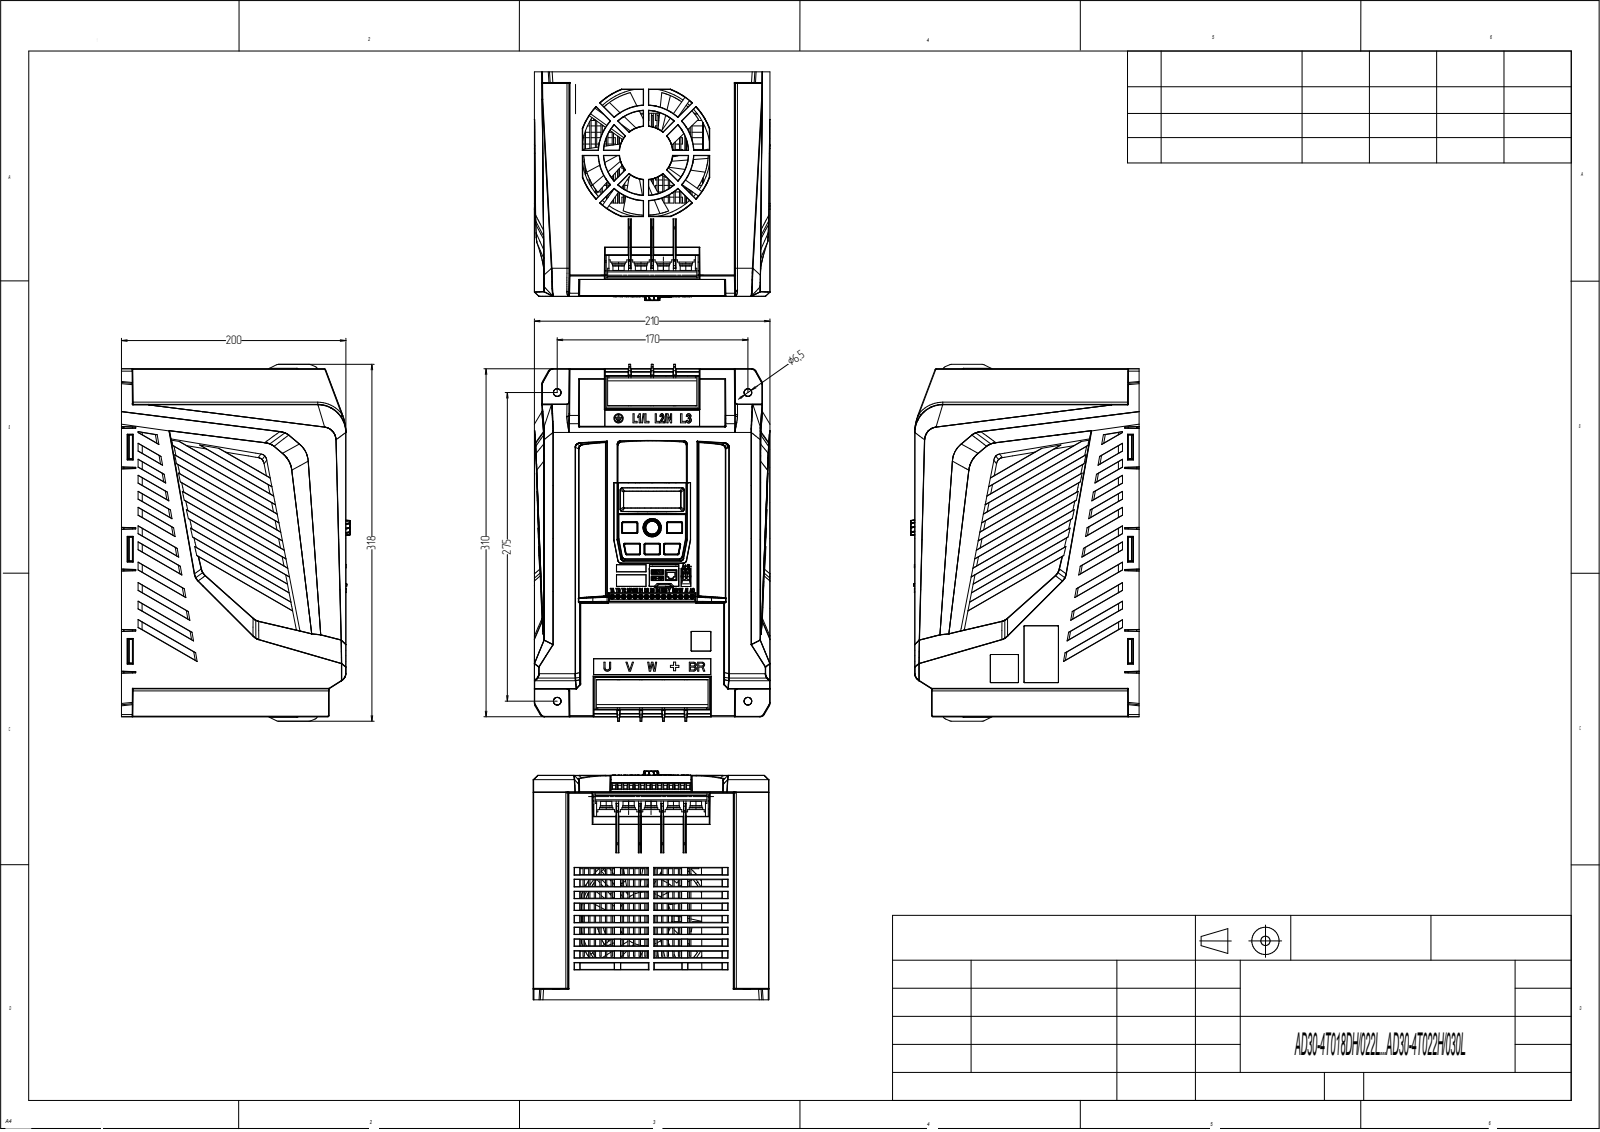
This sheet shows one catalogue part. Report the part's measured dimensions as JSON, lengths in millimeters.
{"part_name": "it3F445D75qg3i", "step_written_by": "SIEMENS PLM Software NX 10.0 (AP203_CONFIGURATION_CONTROLLED_3D_DESIGN_OF_MECHANICAL_PARTS_AND_ASSEMBLIES_MIM_LF)", "units": "millimeters", "bodies": {"solids": 137, "faces": 14429, "planar": 9729, "cylindrical": 2018, "other": 2682}, "overall_size": [318, 210, 203.79], "volume_mm3": 3156000, "surface_area_mm2": 2460000, "round_holes": [[4.1, 19], [1.4, 16], [3.1, 15], [5, 9], [6.1, 9], [6.4, 9], [4.5, 8], [3.7, 5], [2, 4], [3.3, 4], [3.5, 4], [4.3, 4]], "round_bosses_or_shafts": [[0.5, 58], [1, 28], [4.2, 16], [3, 15], [9, 13], [6, 10], [12, 9], [10.7, 9]], "partial_cylinders_radius": [[0.5, 356], [1, 177], [0.3, 166], [2, 110], [0.2, 96], [3, 32], [1.5, 25], [0.1, 22]], "face_to_face_distances": [15, 10, 5, 20, 25, 3.8, 6.2, 1.2, 11.2, 30], "hole_center_spacings": [74.25, 105, 11.83, 14.57, 134.6, 6.93, 7.95, 8.19]}
